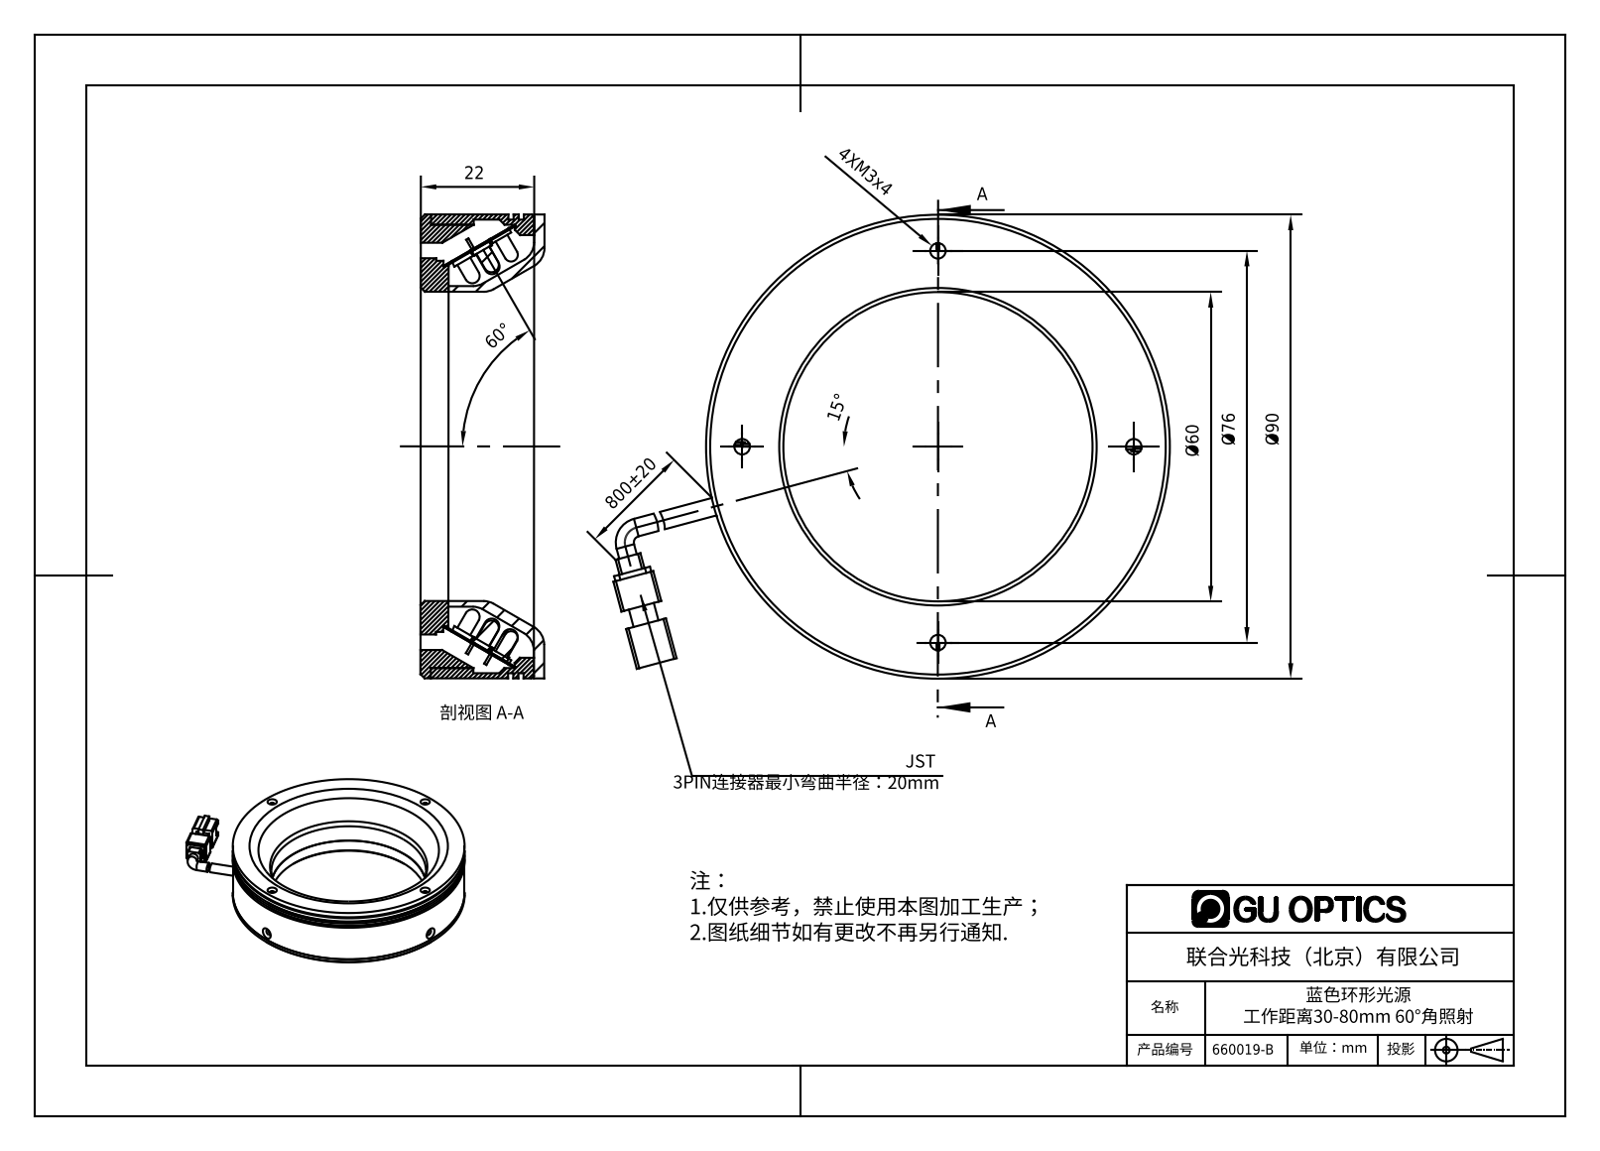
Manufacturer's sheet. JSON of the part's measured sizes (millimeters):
{"part_name": "660019-B", "step_written_by": "SolidWorks 2016 (AUTOMOTIVE_DESIGN)", "units": "millimeters", "bodies": {"solids": 153, "faces": 2753, "planar": 1844, "cylindrical": 708, "other": 201}, "overall_size": [116.8, 90, 24.45], "volume_mm3": 46795, "surface_area_mm2": 61171, "round_holes": [[1.25, 4], [1.7, 4], [3, 4], [3.5, 3], [2, 2], [2.4, 2], [60, 1], [82, 1], [86, 1]], "round_bosses_or_shafts": [[3.8, 147], [3, 147], [3.5, 2], [90, 1], [88, 1], [72, 1], [70, 1], [62.2, 1]], "partial_cylinders_radius": [[0.5, 8], [1, 4], [1.65, 1], [5, 1]], "face_to_face_distances": [2, 22, 1, 24, 3, 20, 5.4, 16.6, 18.6, 3.4], "hole_center_spacings": [30.84, 73.93, 38, 42, 53.74, 59.4, 76, 84]}
